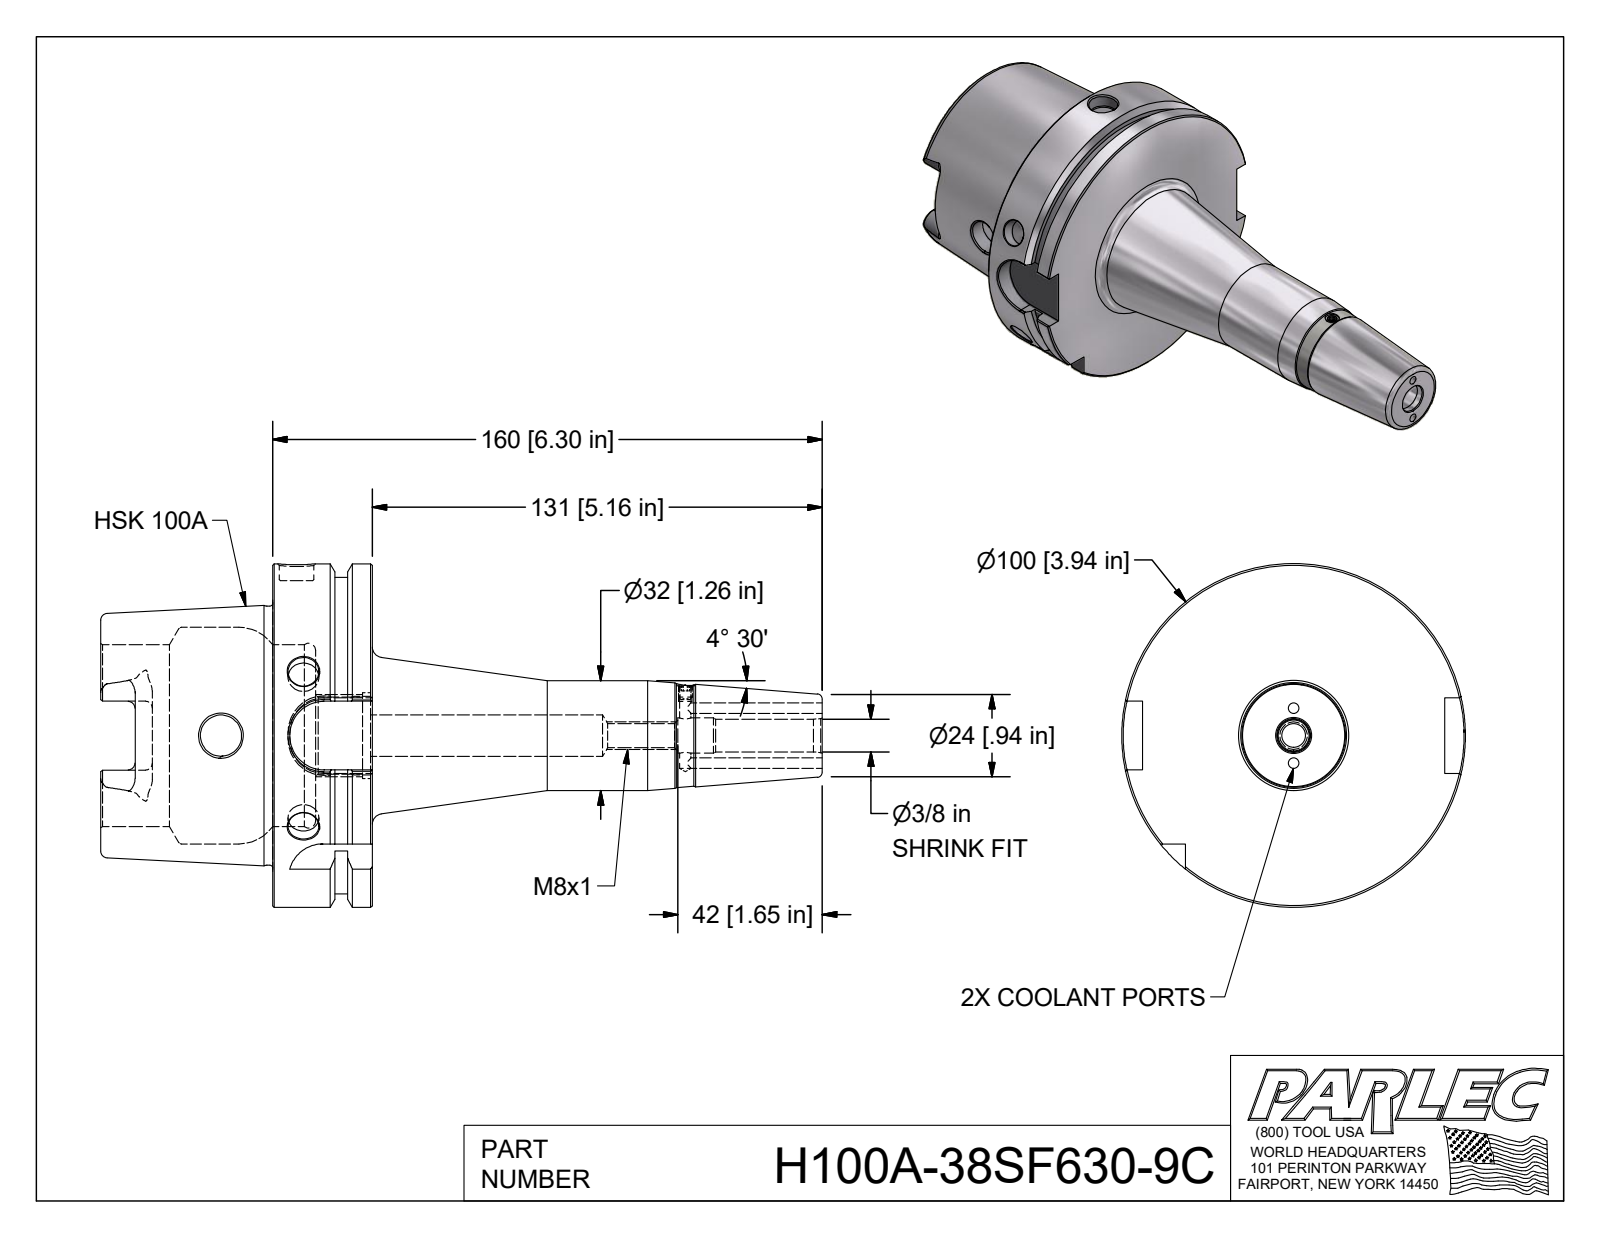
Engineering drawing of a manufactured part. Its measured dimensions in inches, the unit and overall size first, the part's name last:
Units: inches
Overall size (bounding box): 8.268 × 3.937 × 3.937
Round holes (diameter × count): ⌀0.118 ×2, ⌀0.354 ×2, ⌀0.472 ×2, ⌀0.128 ×1, ⌀0.197 ×1, ⌀0.272 ×1, ⌀0.374 ×1, ⌀0.394 ×1, ⌀0.404 ×1, ⌀0.881 ×1, ⌀0.985 ×1, ⌀2.087 ×1
Round bosses / shafts (diameter × count): ⌀3.937 ×1, ⌀3.622 ×1, ⌀2.967 ×1, ⌀1.26 ×1
Partial cylindrical surfaces — rounded edges, fillets, slot ends (radius × count): R0.079 ×6, R0.192 ×4, R0.394 ×4
Main face-to-face distances: 1.142, 0.492, 0.65, 1.969, 2.461, 3.11, 3.465, 2.83, 0.861, 0.369
Hole centre spacings: 0.315, 0.63, 4.454
Volume: 21.89 in³ · Surface area: 104.5 in²
Bodies: 1 solid, 155 faces (49 planar, 42 cylindrical, 64 other)
STEP written by: Autodesk Inventor 2018 (AUTOMOTIVE_DESIGN)
